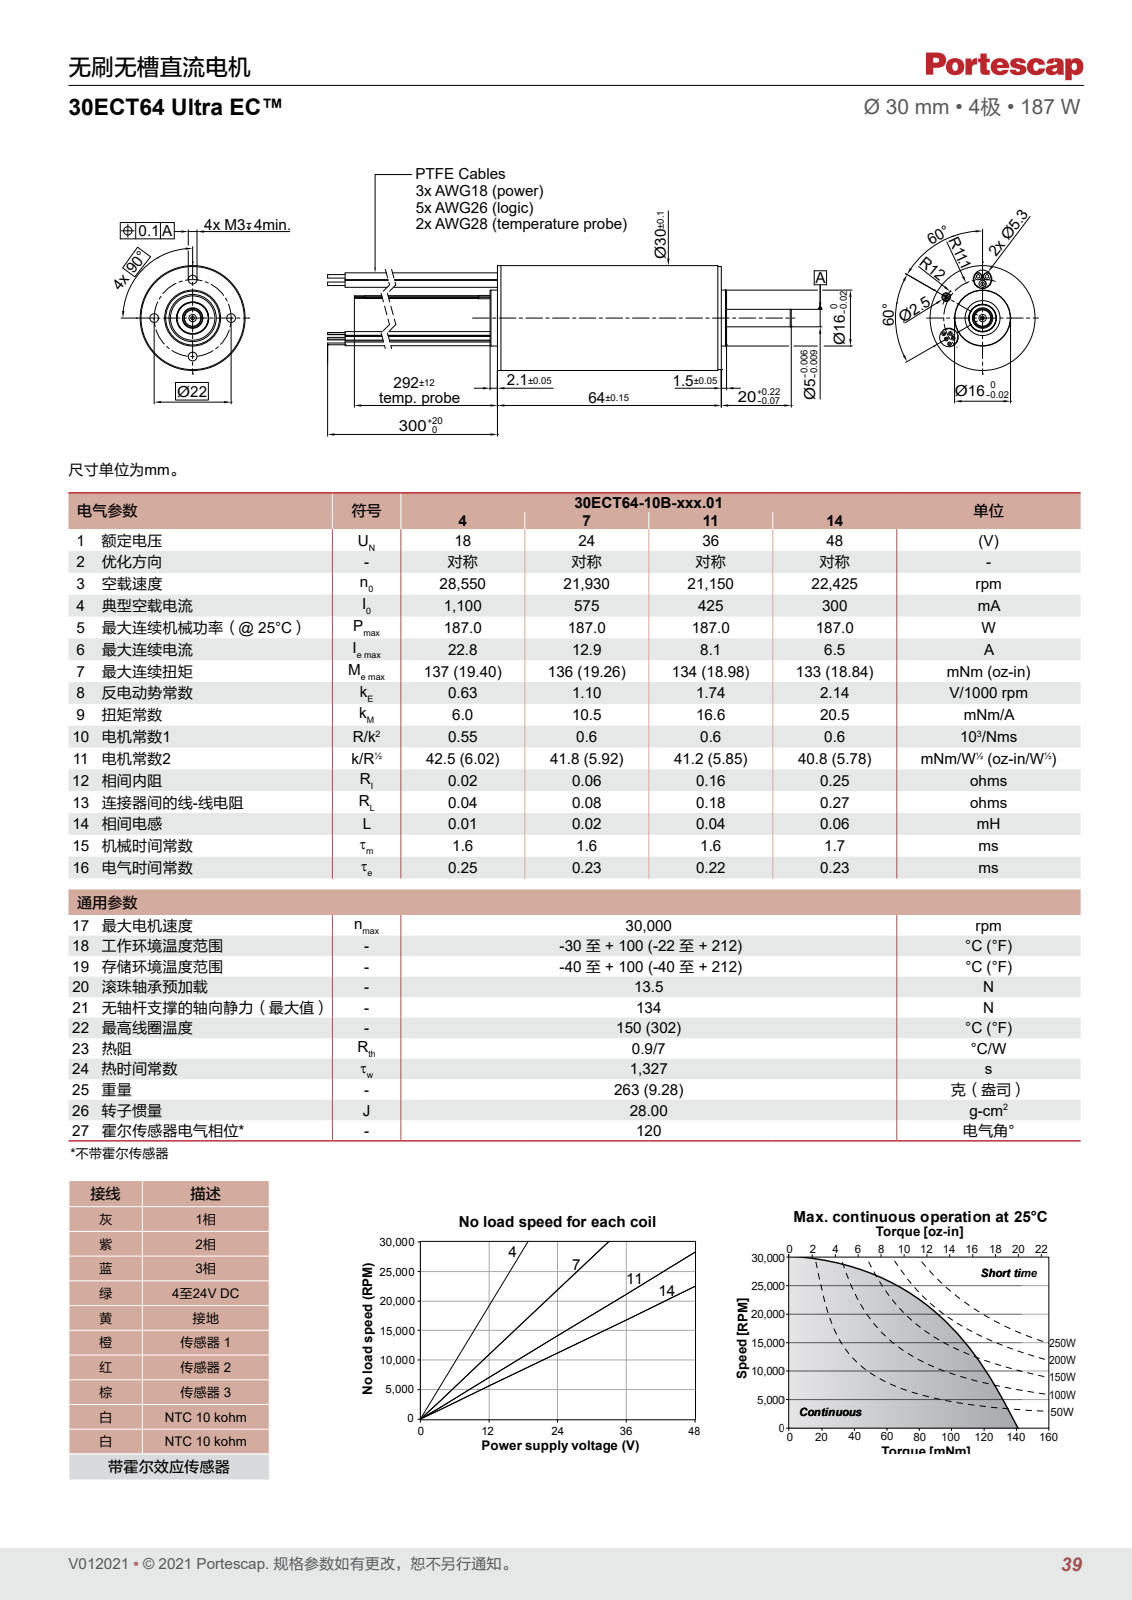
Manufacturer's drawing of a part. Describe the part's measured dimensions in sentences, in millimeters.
The part is named "7011905340". Its 3-D file was written by "SolidWorks 2018 (AUTOMOTIVE_DESIGN)". It is 40 solids with 193 faces: 65 planar, 59 cylindrical and 69 other. Overall it measures 384 by 30 by 30 millimeters. Its volume is 48 669 cubic millimeters and its surface area 35 708 square millimeters. Round holes: 5 of diameter 2.5, 2 of diameter 5.3, 1 of diameter 1, 1 of diameter 5, 1 of diameter 7.91, 1 of diameter 9.25, 1 of diameter 10, 1 of diameter 10.1, 1 of diameter 12.7, 1 of diameter 13, 1 of diameter 13.5. Round bosses or shafts: 5 of diameter 0.5, 3 of diameter 2, 3 of diameter 1, 2 of diameter 0.45, 2 of diameter 0.32, 2 of diameter 0.25, 1 of diameter 30, 1 of diameter 29.5. The main face-to-face distances are 54.1, 6, 60.1, 1.4, 3.9, 58, 64, 2.5, 55.5, 61.5. The hole center spacings are 11, 15.56, 11.1, 15.63, 22, 5.72, 6.03, 11.05.
